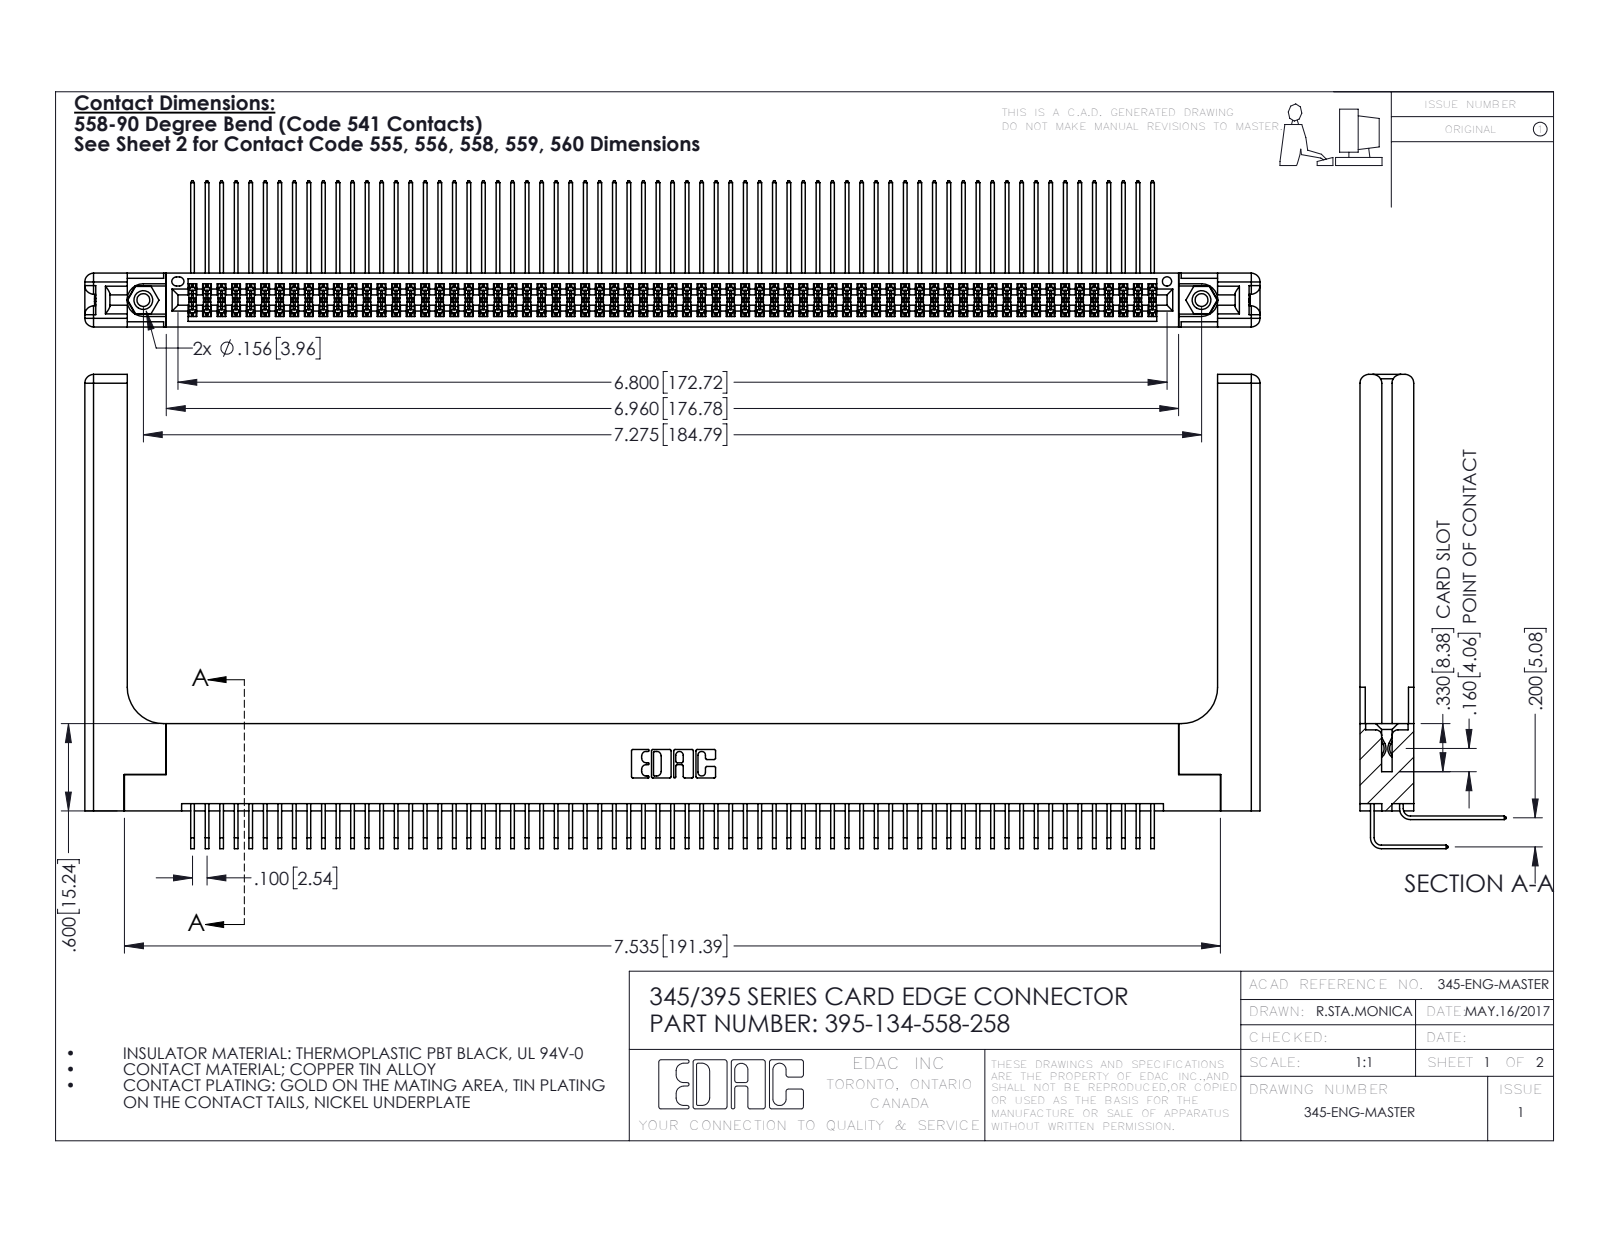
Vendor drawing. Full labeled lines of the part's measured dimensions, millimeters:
Part name (STEP PRODUCT): 345-250-001_345-250-001-102; 345-292-001_558 Tail - 2; 345-292-001_558 559 Tail - 1; 345 Part_Flush Mounting Lugs - 0.156 Dia-TH (+2 more)
STEP written by: SolidWorks 2016 (CONFIG_CONTROL_DESIGN)
Units: millimetres
Bodies: 139 solids, 7350 faces (4918 planar, 2372 cylindrical, 60 other)
Overall size (bounding box): 205.2 × 82.8 × 25.5
Volume: 29 410 mm³ · Surface area: 40 130 mm²
Round holes (diameter × count): ⌀2.3 ×2, ⌀3.2 ×2, ⌀4 ×2, ⌀1.6 ×1
Round bosses / shafts (diameter × count): ⌀3.9 ×2
Partial cylindrical surfaces — rounded edges, fillets, slot ends (radius × count): R0.2 ×202, R0.3 ×22, R1.5 ×16, R0.2 ×6, R0.8 ×6, R0.7 ×3, R0.4 ×2, R0.5 ×2
Main face-to-face distances: 1.8, 7.6, 5.1, 9.4, 2.5, 6.9, 0.6, 5.7, 0.6, 7.2
Hole centre spacings: 6.9, 178.8, 184.8
